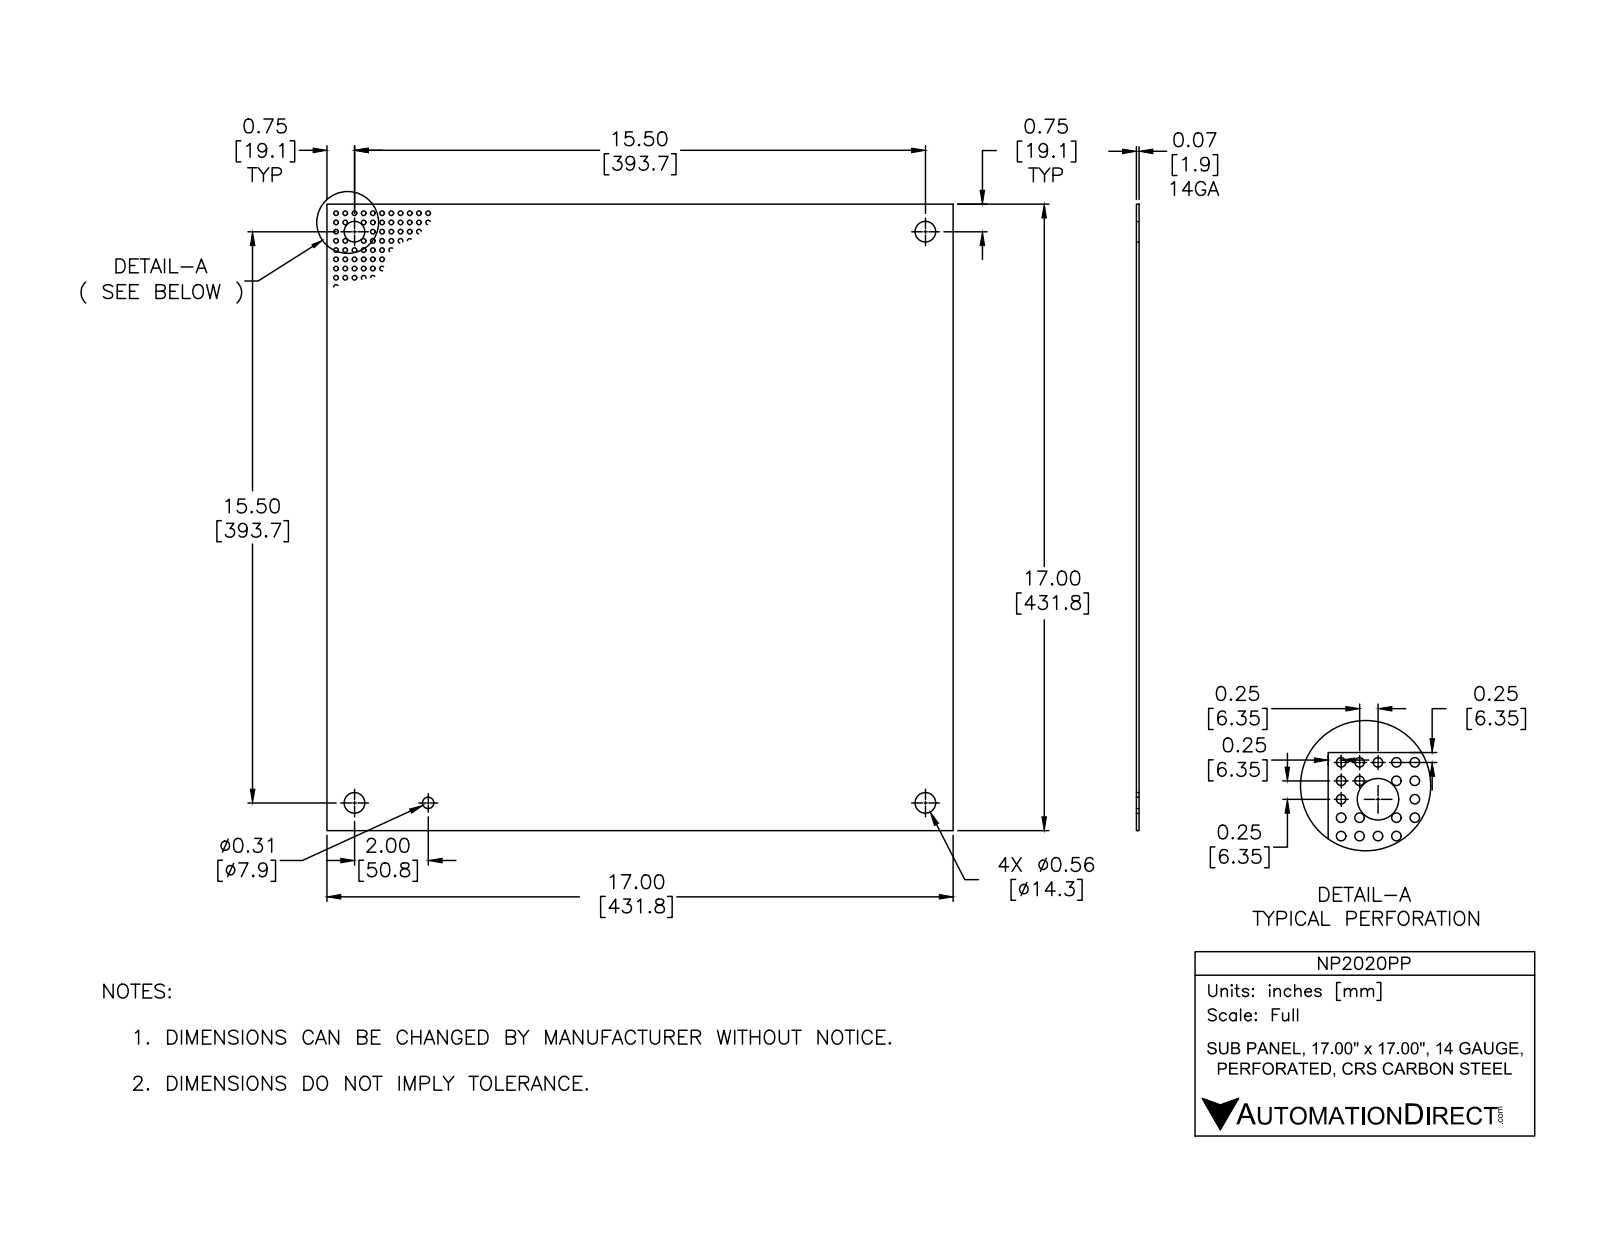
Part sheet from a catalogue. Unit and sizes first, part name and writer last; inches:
Units: inches
Overall size (bounding box): 17 × 17 × 0.074
Round holes (diameter × count): ⌀0.563 ×4, ⌀0.31 ×1
Main face-to-face distances: 0.074, 17
Hole centre spacings: 15.25, 2, 13.25, 15.25, 15.381, 20.202, 21.567, 21.567
Volume: 21.31 in³ · Surface area: 581.5 in²
Bodies: 1 solid, 11 faces (6 planar, 5 cylindrical, 0 other)
Part name (STEP PRODUCT): NP2020PP
STEP written by: Autodesk Inventor 2012 (AUTOMOTIVE_DESIGN)
